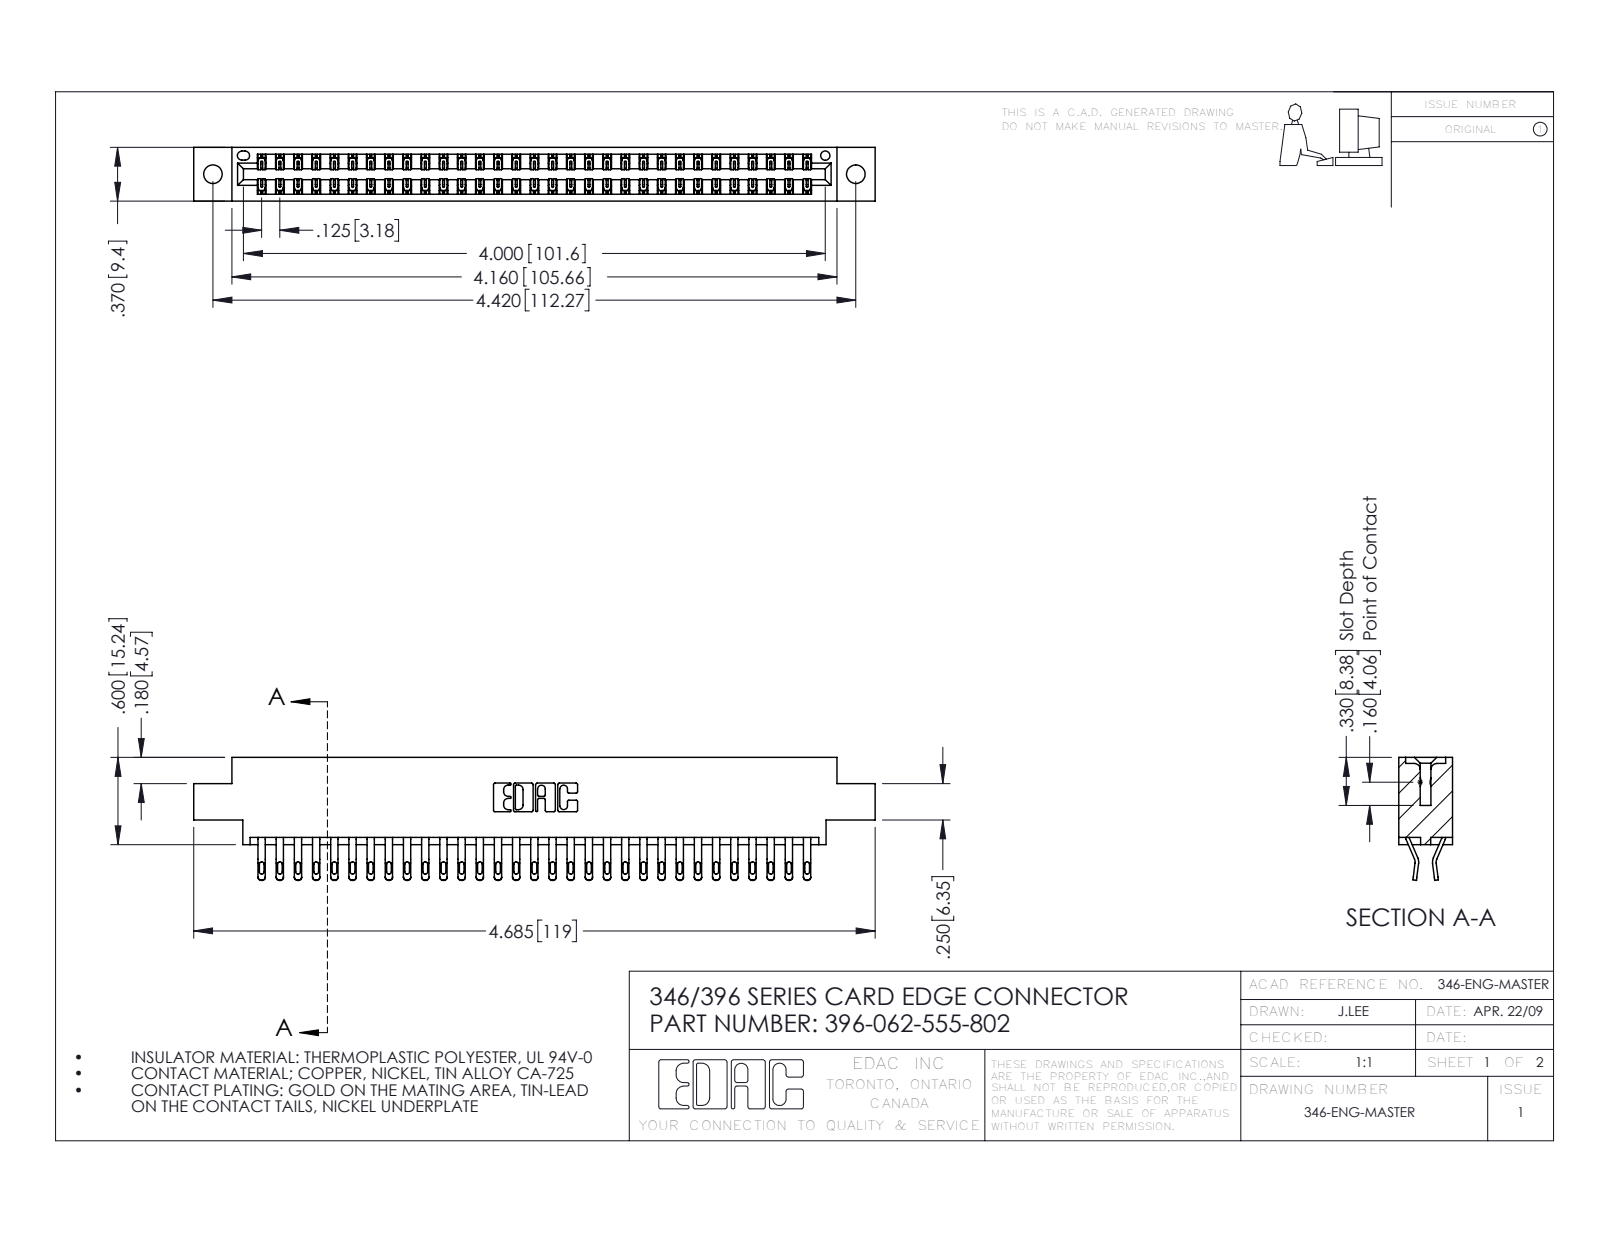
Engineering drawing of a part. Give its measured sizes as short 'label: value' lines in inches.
name: 346 Part_0.170 Offset - 0.128 Dia; 396-062-555-802; 345-292-001_555 Tail
written by: SolidWorks 2016 (CONFIG_CONTROL_DESIGN)
unit: in
bodies: 63 solids, 3722 faces (2126 planar, 1596 cylindrical, 0 other)
size: 4.685 × 0.845 × 0.37
volume: 0.702 in³; area: 25.1 in²
holes: 2× ⌀0.128, 1× ⌀0.064
rounds: 124× R0.016, 124× R0.02, 93× R0.006, 22× R0.01, 6× R0.007, 6× R0.031, 3× R0.026, 2× R0.01
face distances: 0.048, 0.322, 0.37, 0.25, 0.025, 0.072, 0.298, 0.275, 0.148, 0.222
hole spacings: 0.246, 4.212, 4.42
